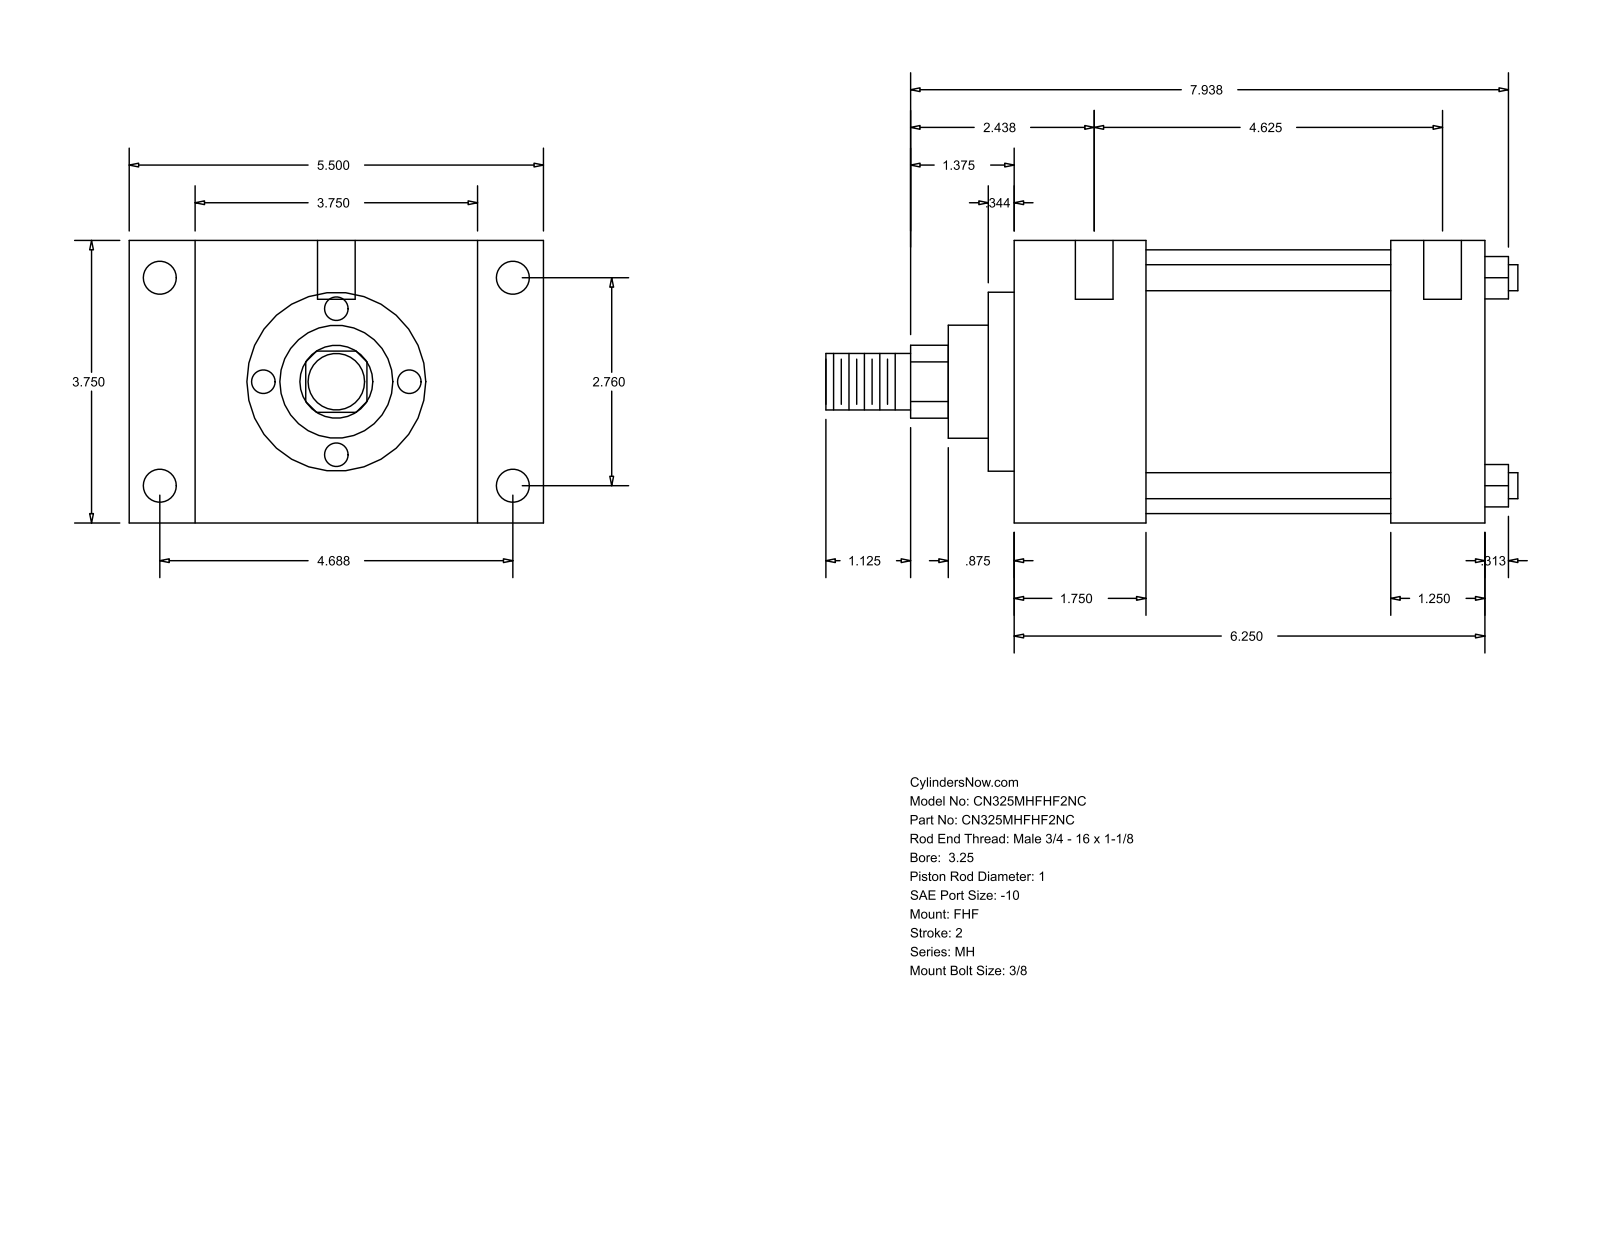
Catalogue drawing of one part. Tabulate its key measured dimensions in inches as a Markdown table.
| quantity | value |
| --- | --- |
| part name | MH_FHF__0325_1 |
| STEP written by | GSSL Pune (CONFIG_CONTROL_DESIGN) |
| units | inches |
| bodies | 0 solids, 90 faces (61 planar, 29 cylindrical, 0 other) |
| overall size | 9.187 × 5.5 × 3.75 |
| round holes (diameter × count) | 0.219 × 4, 0.438 × 4, 0.5 × 2 |
| round bosses / shafts (diameter × count) | 0.345 × 4, 3.5 × 1, 2.375 × 1, 1.5 × 1, 1 × 1, 0.75 × 1 |
| partial cylindrical surfaces (radius × count) | 0.484 × 1 |
| main face-to-face distances | 3.75, 6.25, 1.75, 4.5, 0.875, 4.625, 5.5, 5, 3.25, 1.25 |
| hole center spacings | 4.687, 2.76, 4.875, 5.439, 0.062, 0.187, 4.625, 4.813 |
